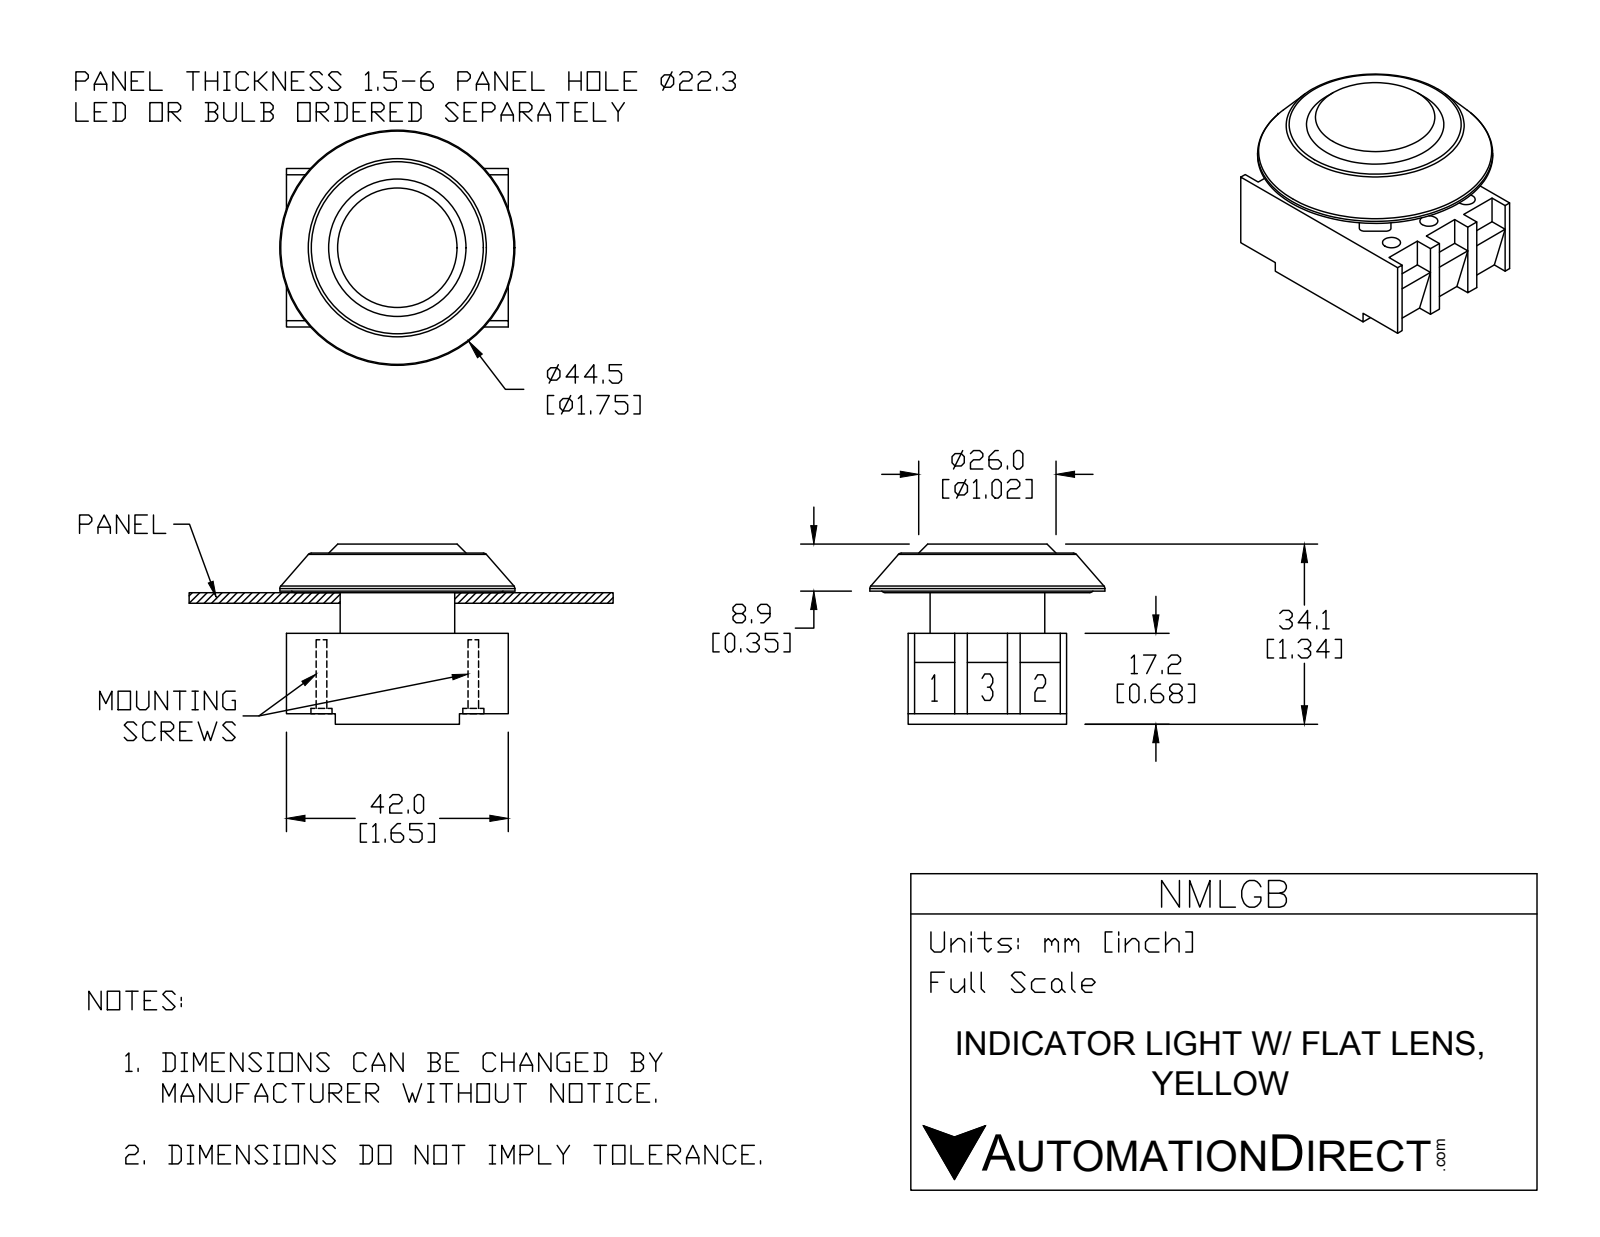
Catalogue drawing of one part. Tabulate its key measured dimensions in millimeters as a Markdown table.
| quantity | value |
| --- | --- |
| part name | NMLGB |
| STEP written by | SolidWorks 2015 (AUTOMOTIVE_DESIGN) |
| units | millimeters |
| bodies | 6 solids, 209 faces (125 planar, 63 cylindrical, 21 other) |
| overall size | 44.5 × 44.5 × 34.1 |
| volume | 23 947 mm³ |
| surface area | 15 137 mm² |
| round holes (diameter × count) | 3.4 × 6, 5 × 6, 12.5 × 1 |
| round bosses / shafts (diameter × count) | 4.6 × 2, 4 × 2, 44.5 × 1, 21.7 × 1 |
| partial cylindrical surfaces (radius × count) | 1 × 8, 8.7 × 5, 11 × 1 |
| main face-to-face distances | 30, 15.2, 8, 7.7, 9.2, 16.9, 8.9, 22.9, 10, 7.5 |
| hole center spacings | 10, 17.52, 30.45, 28.76, 14.38, 20, 35.03 |
